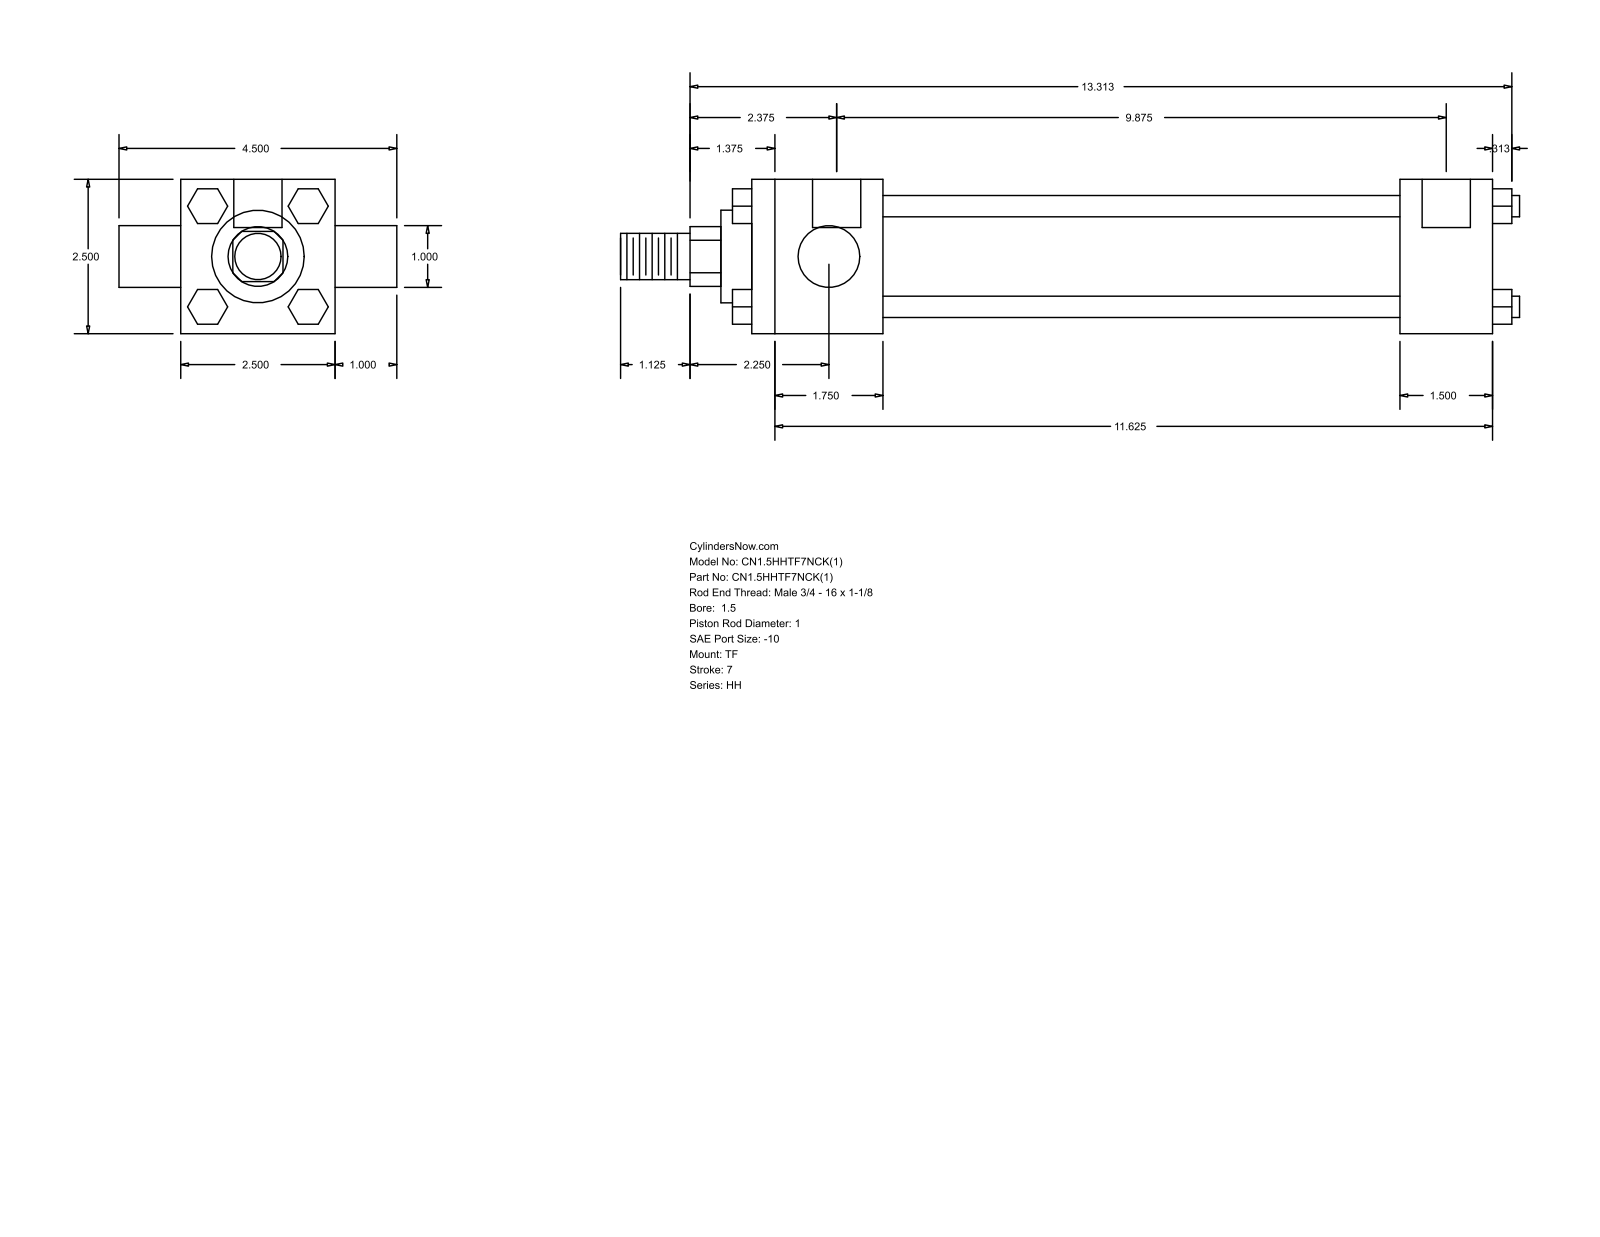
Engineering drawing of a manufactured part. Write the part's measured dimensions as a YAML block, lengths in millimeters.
part_name: "HH_TF__0150_1"
step_written_by: "GSSL Pune (CONFIG_CONTROL_DESIGN)"
units: millimeters
bodies: {solids: 0, faces: 120, planar: 92, cylindrical: 28, other: 0}
overall_size: [369.89, 114.3, 63.5]
round_holes:
  - {diameter: 5.56, count: 3}
  - {diameter: 19.84, count: 2}
round_bosses_or_shafts:
  - {diameter: 8.76, count: 4}
  - {diameter: 25.4, count: 2}
  - {diameter: 44.45, count: 1}
  - {diameter: 38.1, count: 1}
  - {diameter: 19.05, count: 1}
partial_cylinders:
  - {radius: 12.29, count: 1}
face_to_face_distances: [63.5, 38.1, 250.82, 212.72, 53.98, 266.7, 304.8, 25.4, 20.7, 14.29]
hole_center_spacings: [1.59, 252.41, 250.82, 254]
